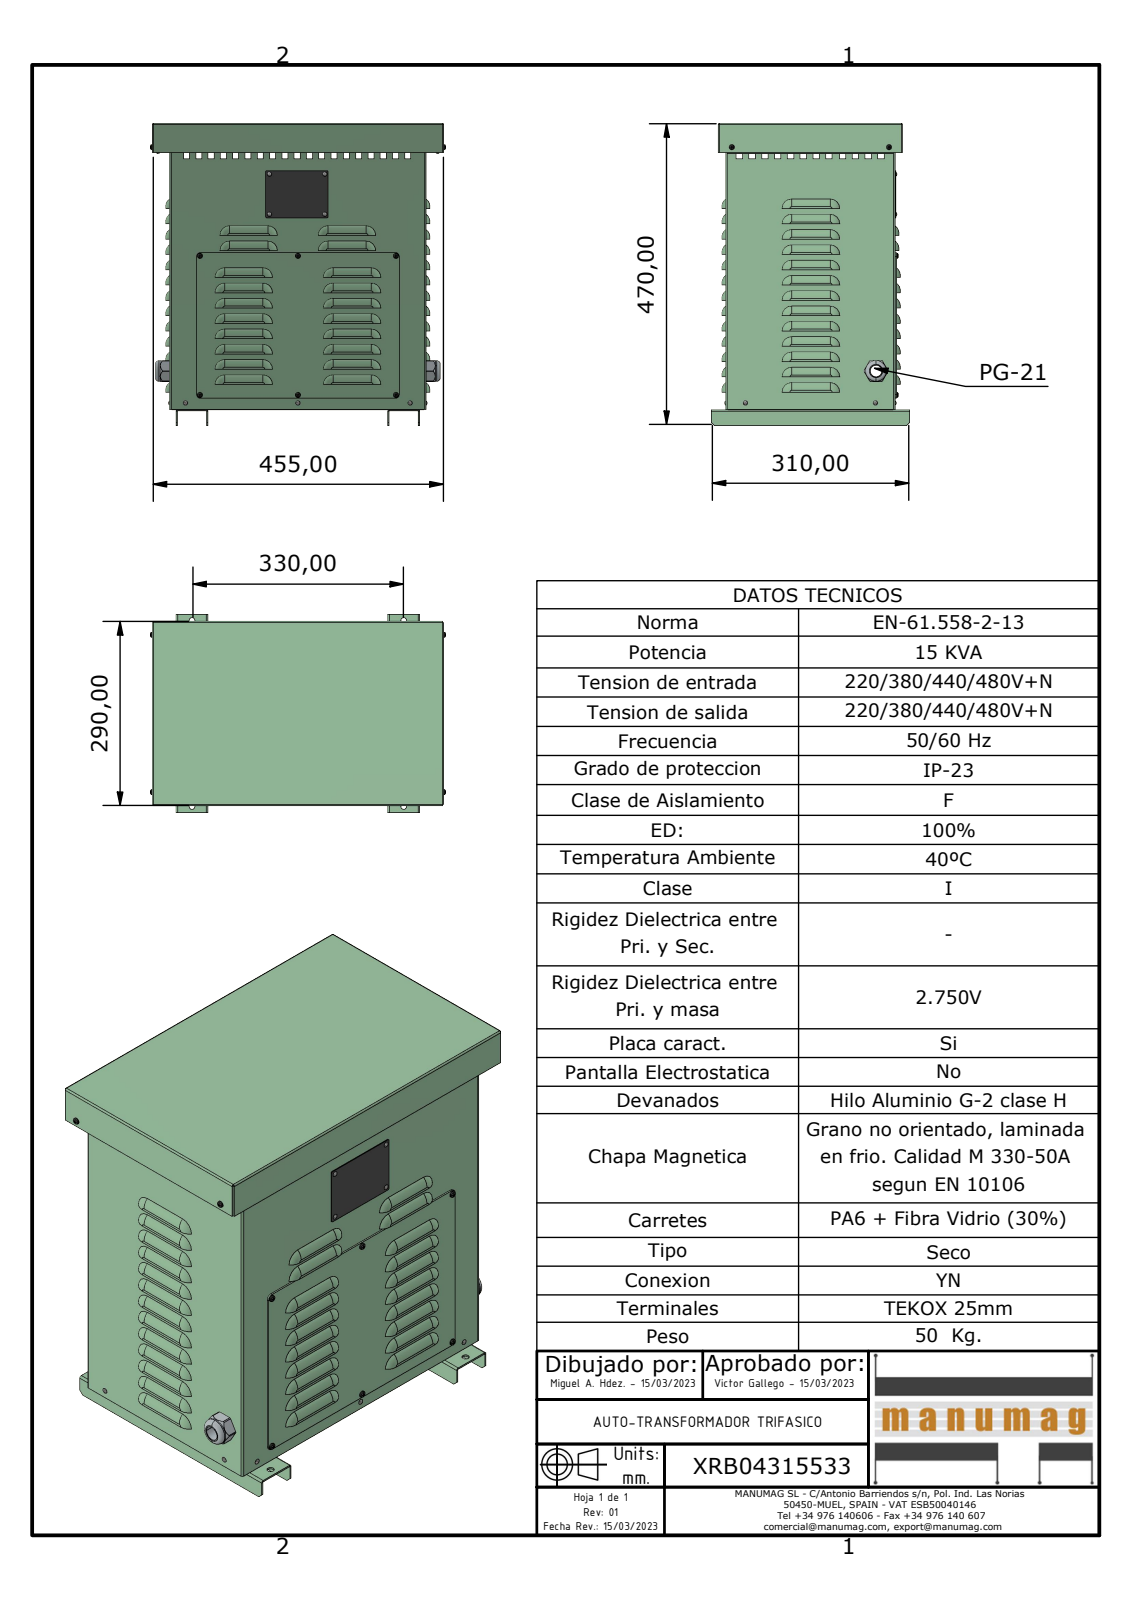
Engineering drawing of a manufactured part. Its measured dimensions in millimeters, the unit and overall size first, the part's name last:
Units: millimetres
Overall size (bounding box): 474.44 × 463.69 × 310
Round holes (diameter × count): ⌀3.4 ×17, ⌀4 ×9, ⌀2.3 ×8, ⌀9 ×6, ⌀5.1 ×3, ⌀8.92 ×2, ⌀18 ×1, ⌀29.9 ×1
Round bosses / shafts (diameter × count): ⌀3.2 ×9, ⌀4 ×8, ⌀3.62 ×8, ⌀32.4 ×1, ⌀28.5 ×1, ⌀28.3 ×1
Partial cylindrical surfaces — rounded edges, fillets, slot ends (radius × count): R14 ×118, R4 ×63, R15 ×49, R2 ×10, R2 ×9, R3.47 ×8, R0.5 ×6, R2.5 ×6
Main face-to-face distances: 2, 262.92, 264.92, 400.8, 447.27, 449.27, 260.92, 398.8, 402.8, 4
Hole centre spacings: 218.1, 153.8, 154.1, 266.87, 267.05, 307.9, 332.28, 377.32
Volume: 2 342 000 mm³ · Surface area: 2 098 000 mm²
Bodies: 33 solids, 2242 faces (1225 planar, 489 cylindrical, 528 other)
Part name (STEP PRODUCT): XRB04315533; JE015 - JE020 - JE025 EXPORT CUERPO; JE015 - JE020 - JE025 EXPORT BASE; JE015 - JE020 - JE025 EXPORT PATA (+6 more)
STEP written by: Autodesk Inventor 2023 (AUTOMOTIVE_DESIGN)
